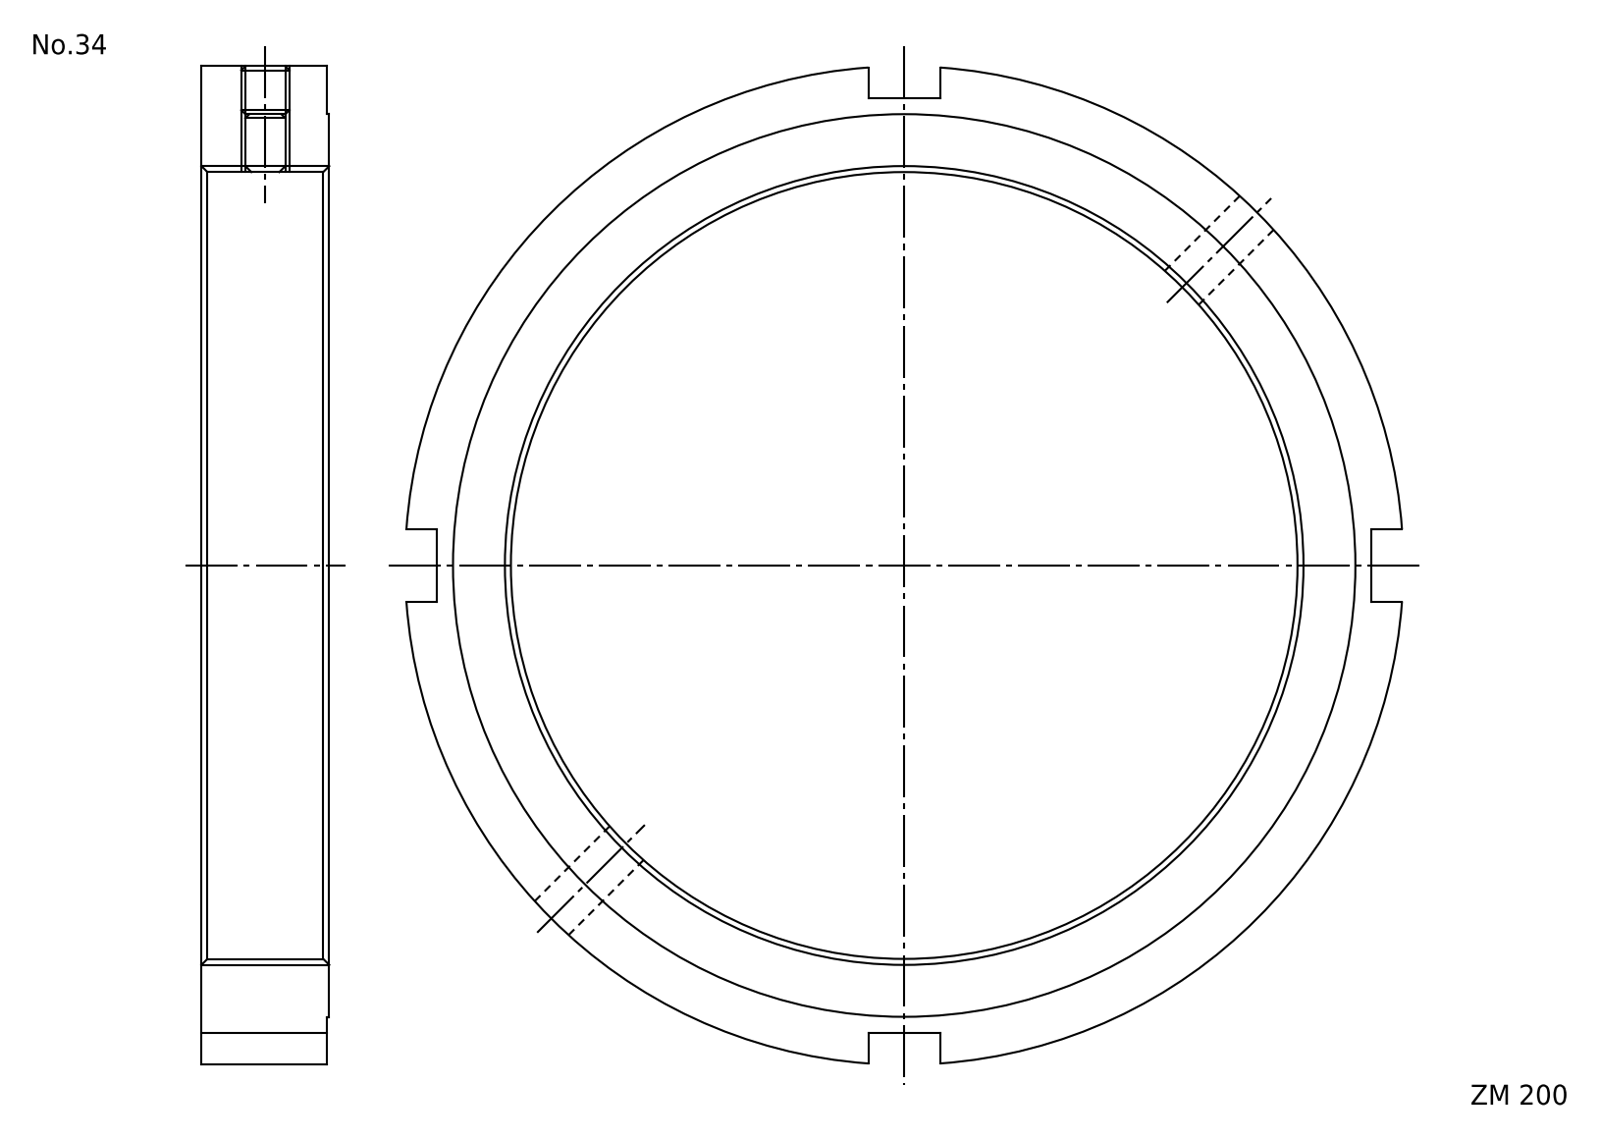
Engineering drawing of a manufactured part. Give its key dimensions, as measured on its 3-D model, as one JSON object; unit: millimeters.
{"part_name": "FKD ZM200", "step_written_by": "Autodesk Inventor 2011 (AUTOMOTIVE_DESIGN)", "units": "millimeters", "bodies": {"solids": 1, "faces": 23, "planar": 15, "cylindrical": 8, "other": 0}, "overall_size": [249.35, 249.35, 32], "volume_mm3": 539092, "surface_area_mm2": 82607, "round_holes": [[10.11, 2], [200, 1]], "round_bosses_or_shafts": [[250, 1], [226, 1]], "face_to_face_distances": [32, 0.5, 31.5, 108, 126, 234, 18]}
